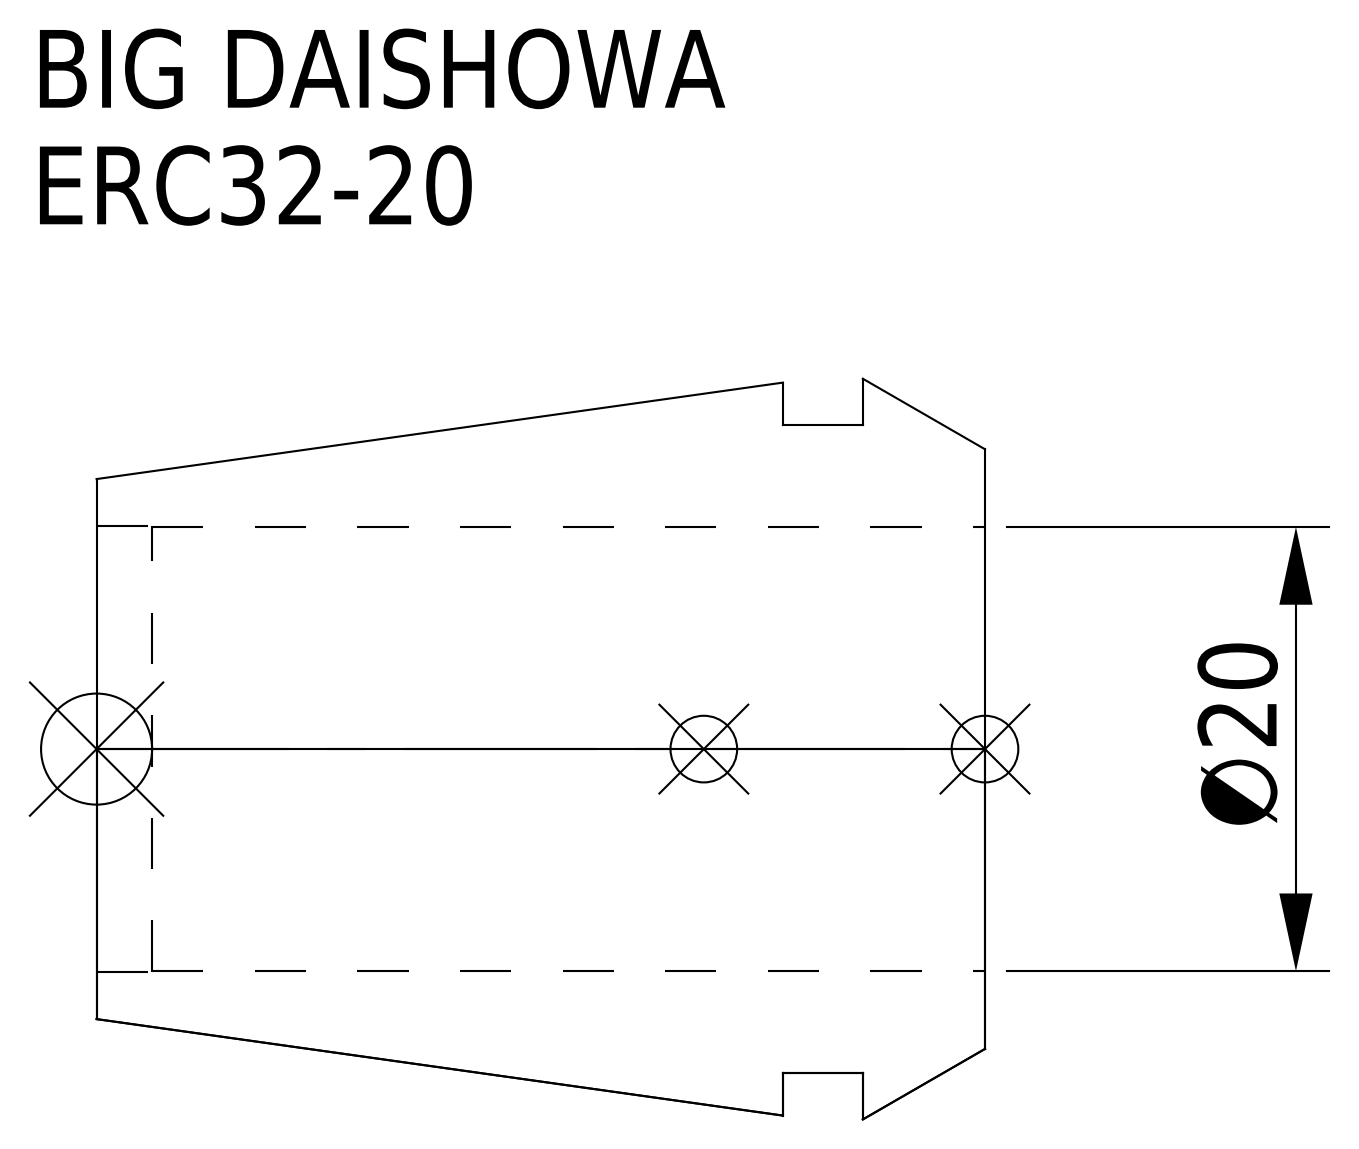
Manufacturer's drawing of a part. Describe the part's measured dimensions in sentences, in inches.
The part is named "ERC32-20". Its 3-D file was written by "CREO PARAMETRIC BY PTC INC, 2016380 (AUTOMOTIVE_DESIGN)". It is 1 solid with 15 faces: 5 planar, 6 cylindrical and 4 other. Overall it measures 1.575 by 1.313 by 1.313 inches. Its volume is 0.847 cubic inches and its surface area 10.93 square inches. Round holes: 1 of diameter 0.787, 1 of diameter 0.789. Round bosses or shafts: 1 of diameter 1.15. The main face-to-face distances are 0.217, 0.358, 0.142, 1.575, 1.358, 1.217, 1.476, 1.26, 1.118, 0.098.
